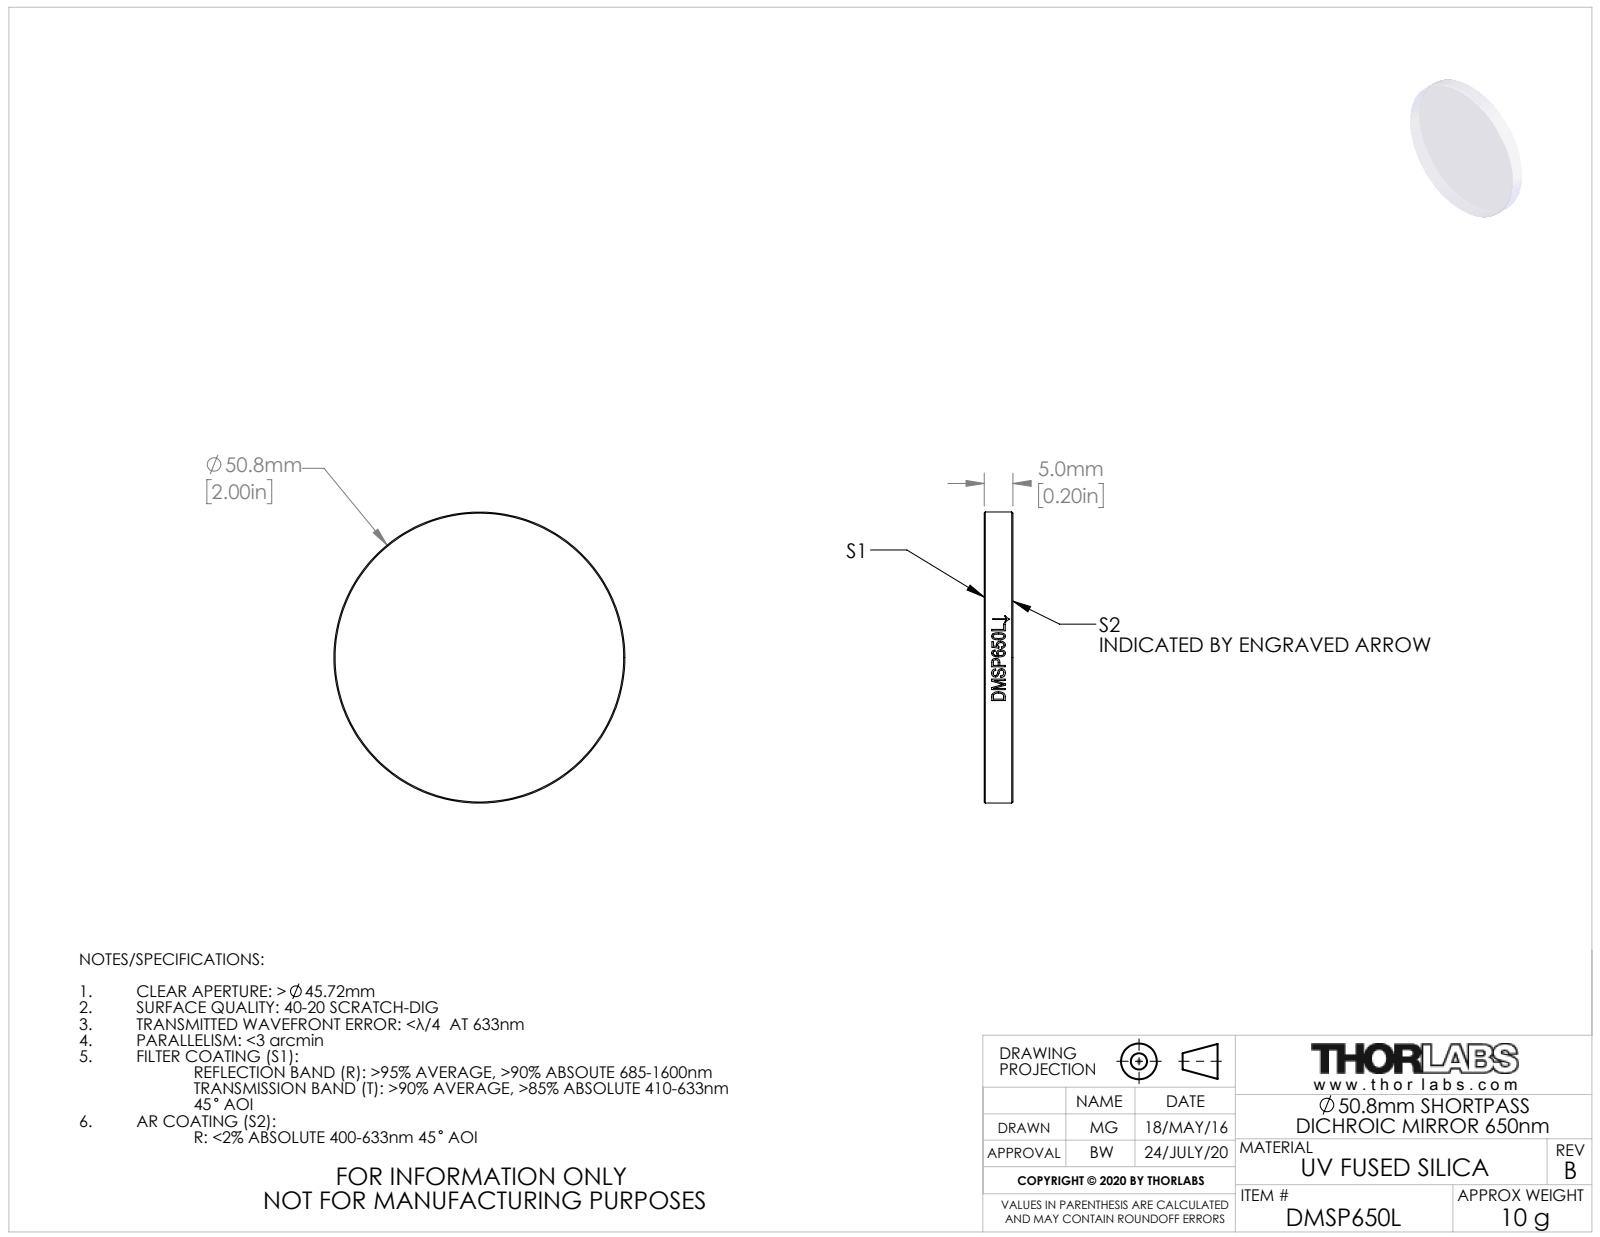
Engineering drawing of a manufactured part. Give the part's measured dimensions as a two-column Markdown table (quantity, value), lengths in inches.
| quantity | value |
| --- | --- |
| part name | TTN045169-E0W |
| STEP written by | SolidWorks 2018 (CONFIG_CONTROL_DESIGN) |
| units | inches |
| bodies | 1 solid, 21 faces (2 planar, 15 cylindrical, 4 other) |
| overall size | 2 × 2 × 0.197 |
| volume | 0.618 in³ |
| surface area | 7.462 in² |
| round bosses / shafts (diameter × count) | 2 × 1 |
| main face-to-face distances | 0.197 |
